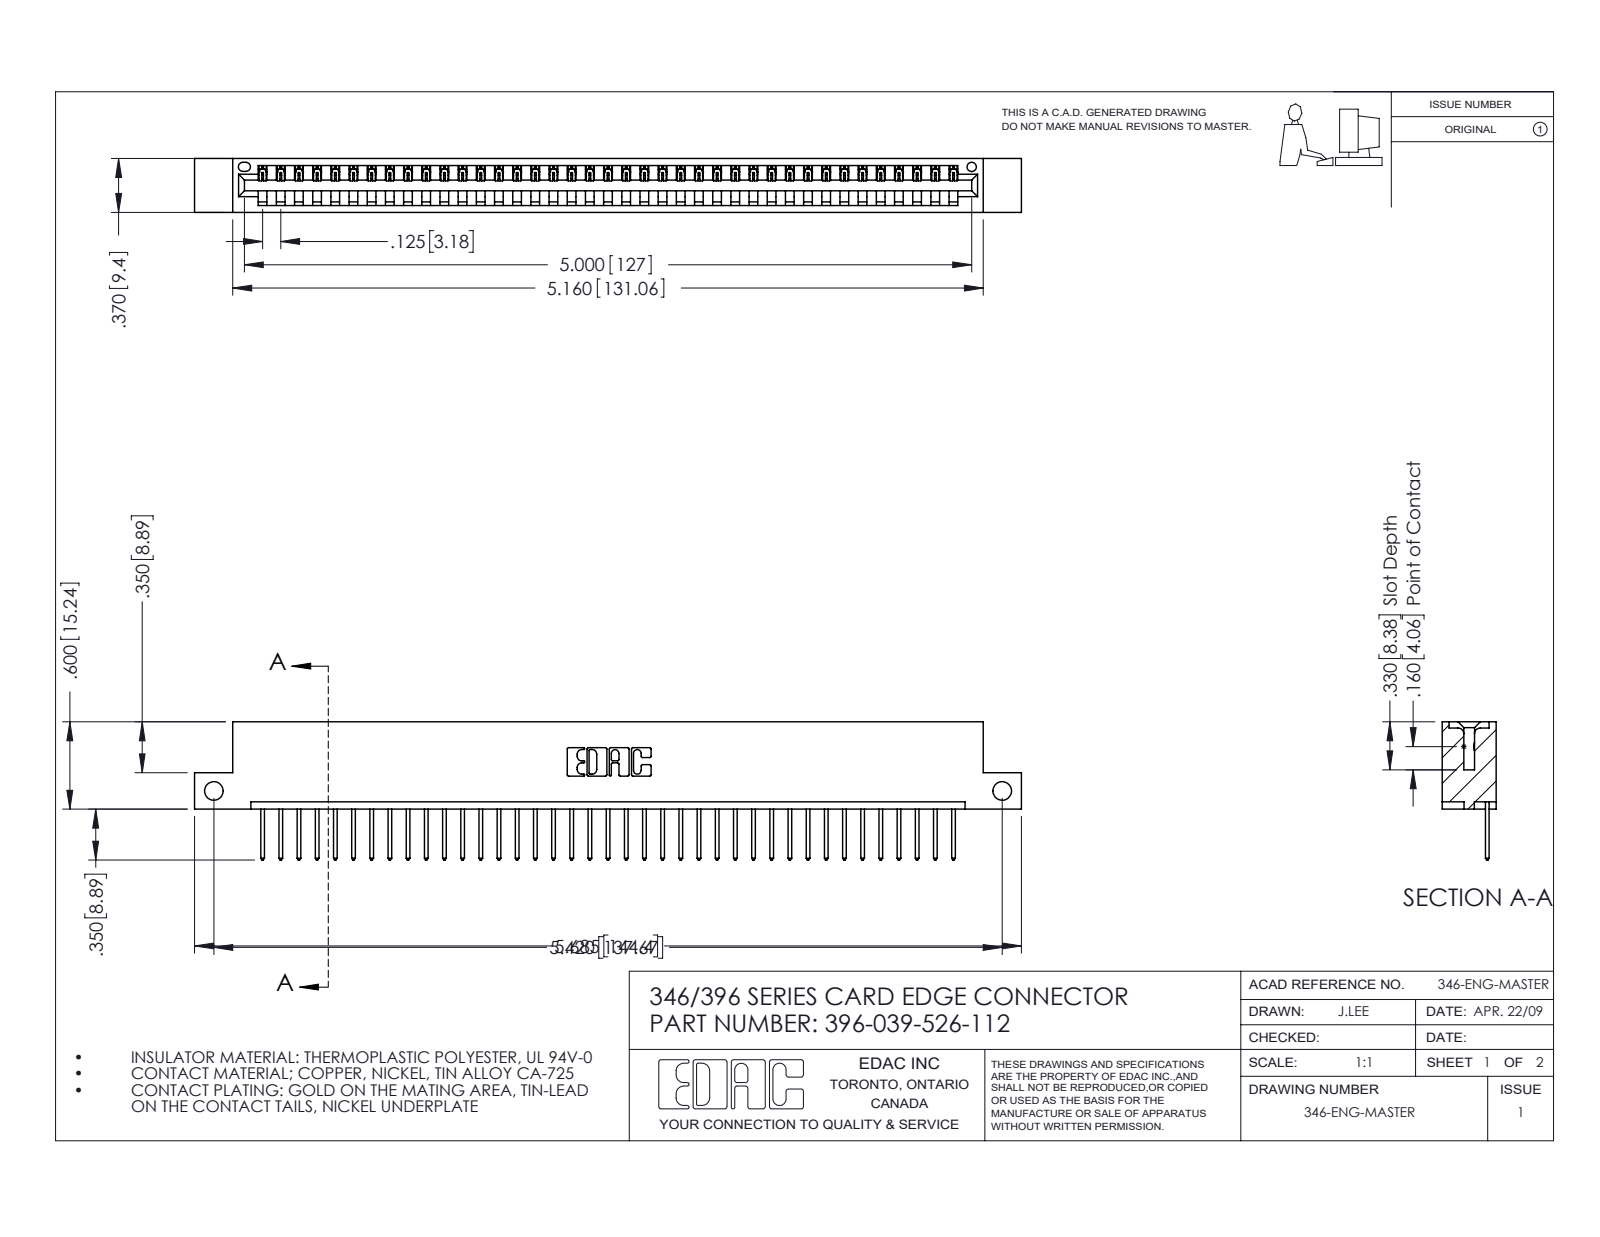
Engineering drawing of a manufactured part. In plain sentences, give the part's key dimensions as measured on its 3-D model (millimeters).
The part is named "396-039-526-112; 345-292-001_345-293-126; 346 Part_Flush Mounting Lugs - Side Mount". Its 3-D file was written by "SolidWorks 2016 (CONFIG_CONTROL_DESIGN)". It is 40 solids with 2384 faces: 1636 planar, 748 cylindrical and 0 other. Overall it measures 144.4 by 24.1 by 9.4 millimeters. Its volume is 13 700 cubic millimeters and its surface area 16 880 square millimeters. Round holes: 2 of diameter 3.3, 1 of diameter 1.6. Partial cylindrical surfaces (rounded edges, fillets, slot ends): 78 of radius 0.2, 78 of radius 0.3, 22 of radius 0.3, 6 of radius 0.2, 6 of radius 0.8, 3 of radius 0.7, 2 of radius 0.8, 2 of radius 1. The main face-to-face distances are 1.2, 8.2, 9.4, 6.4, 1.8, 7.6, 0.6, 3.8, 5.6, 2.5. The hole center spacings are 137.7.
